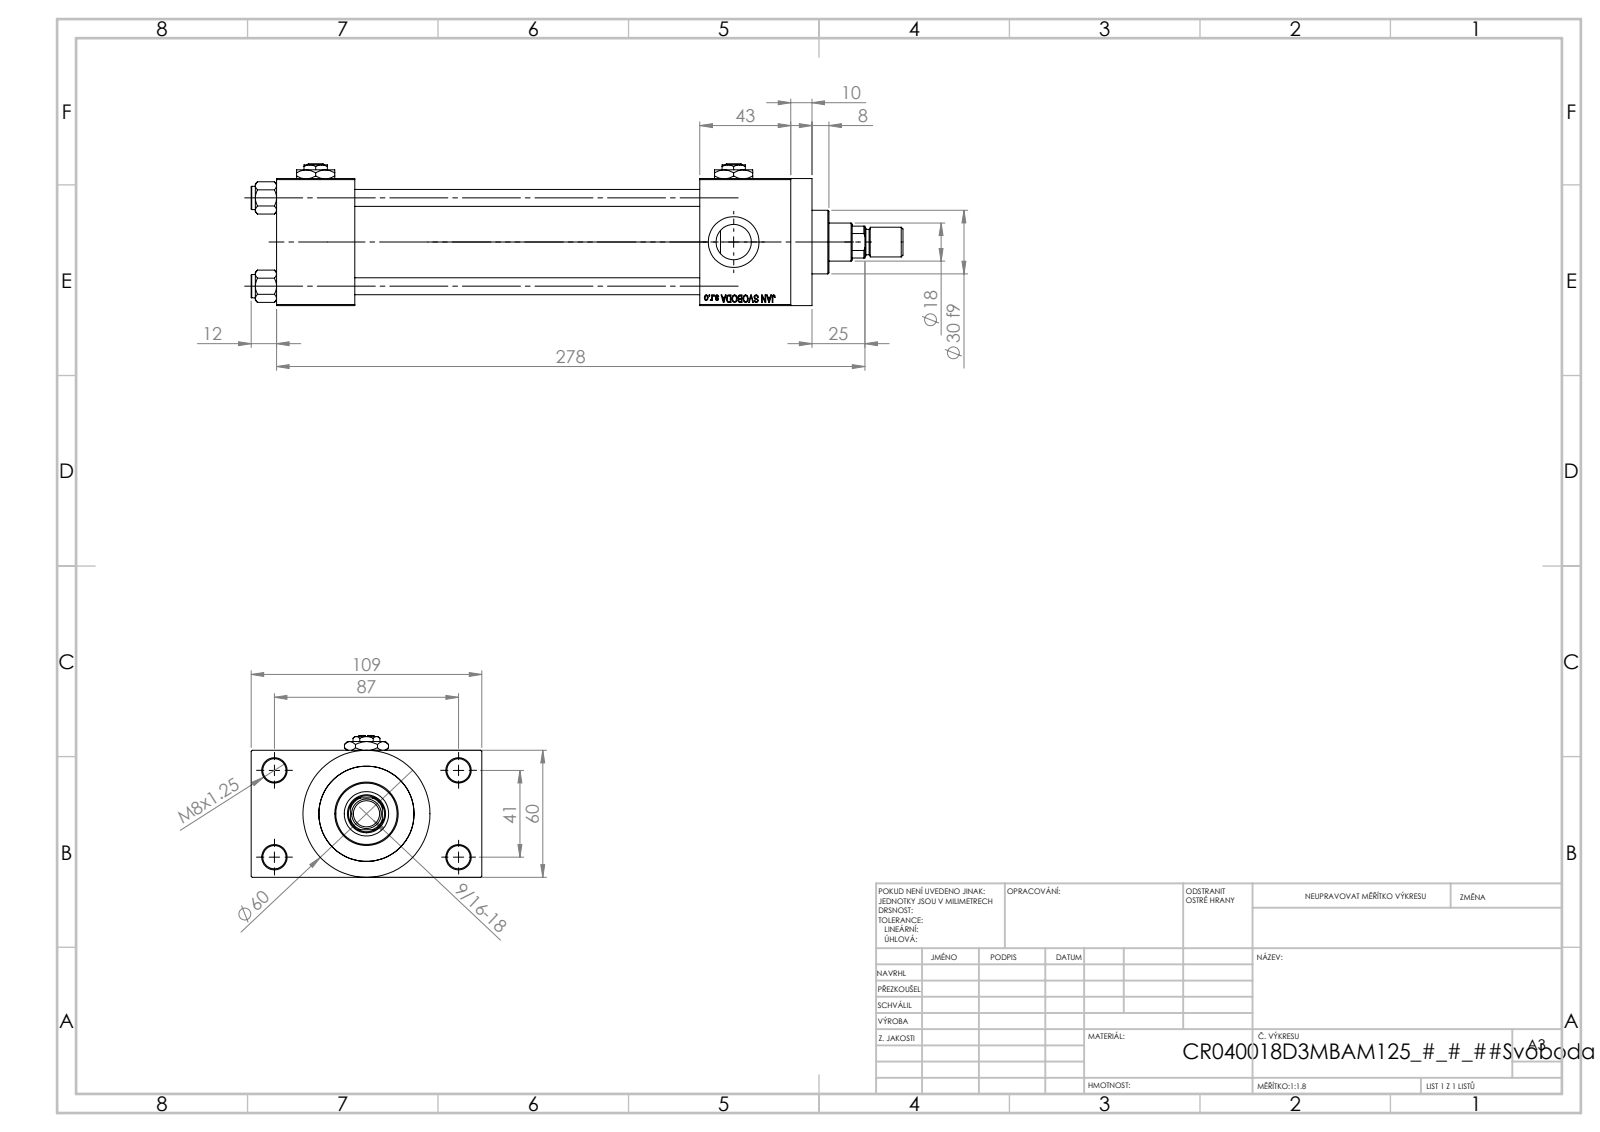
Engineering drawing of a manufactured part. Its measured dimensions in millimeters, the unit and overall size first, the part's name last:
Units: millimetres
Overall size (bounding box): 308 × 109 × 67
Round holes (diameter × count): ⌀8 ×4, ⌀11 ×4, ⌀16.66 ×4, ⌀24 ×4, ⌀7 ×3, ⌀8.5 ×1, ⌀18 ×1, ⌀21 ×1, ⌀31 ×1, ⌀40 ×1, ⌀45 ×1
Round bosses / shafts (diameter × count): ⌀11 ×4, ⌀60 ×1, ⌀46 ×1, ⌀30 ×1, ⌀14 ×1, ⌀12 ×1
Partial cylindrical surfaces — rounded edges, fillets, slot ends (radius × count): R8.5 ×1
Main face-to-face distances: 60, 163, 84.5, 24.5, 37, 200, 43, 243, 206, 53
Hole centre spacings: 22.65, 29.49, 41.7, 47.15, 48.09, 64.35, 76.49, 41
Volume: 603 698 mm³ · Surface area: 171 095 mm²
Bodies: 14 solids, 1219 faces (550 planar, 103 cylindrical, 566 other)
Part name (STEP PRODUCT): V215_VC_A; V215CR_VCP_D; V215CR_D_Body; V215CR_D_TYCINKA (+3 more)
STEP written by: SolidWorks 2019 (CONFIG_CONTROL_DESIGN)
